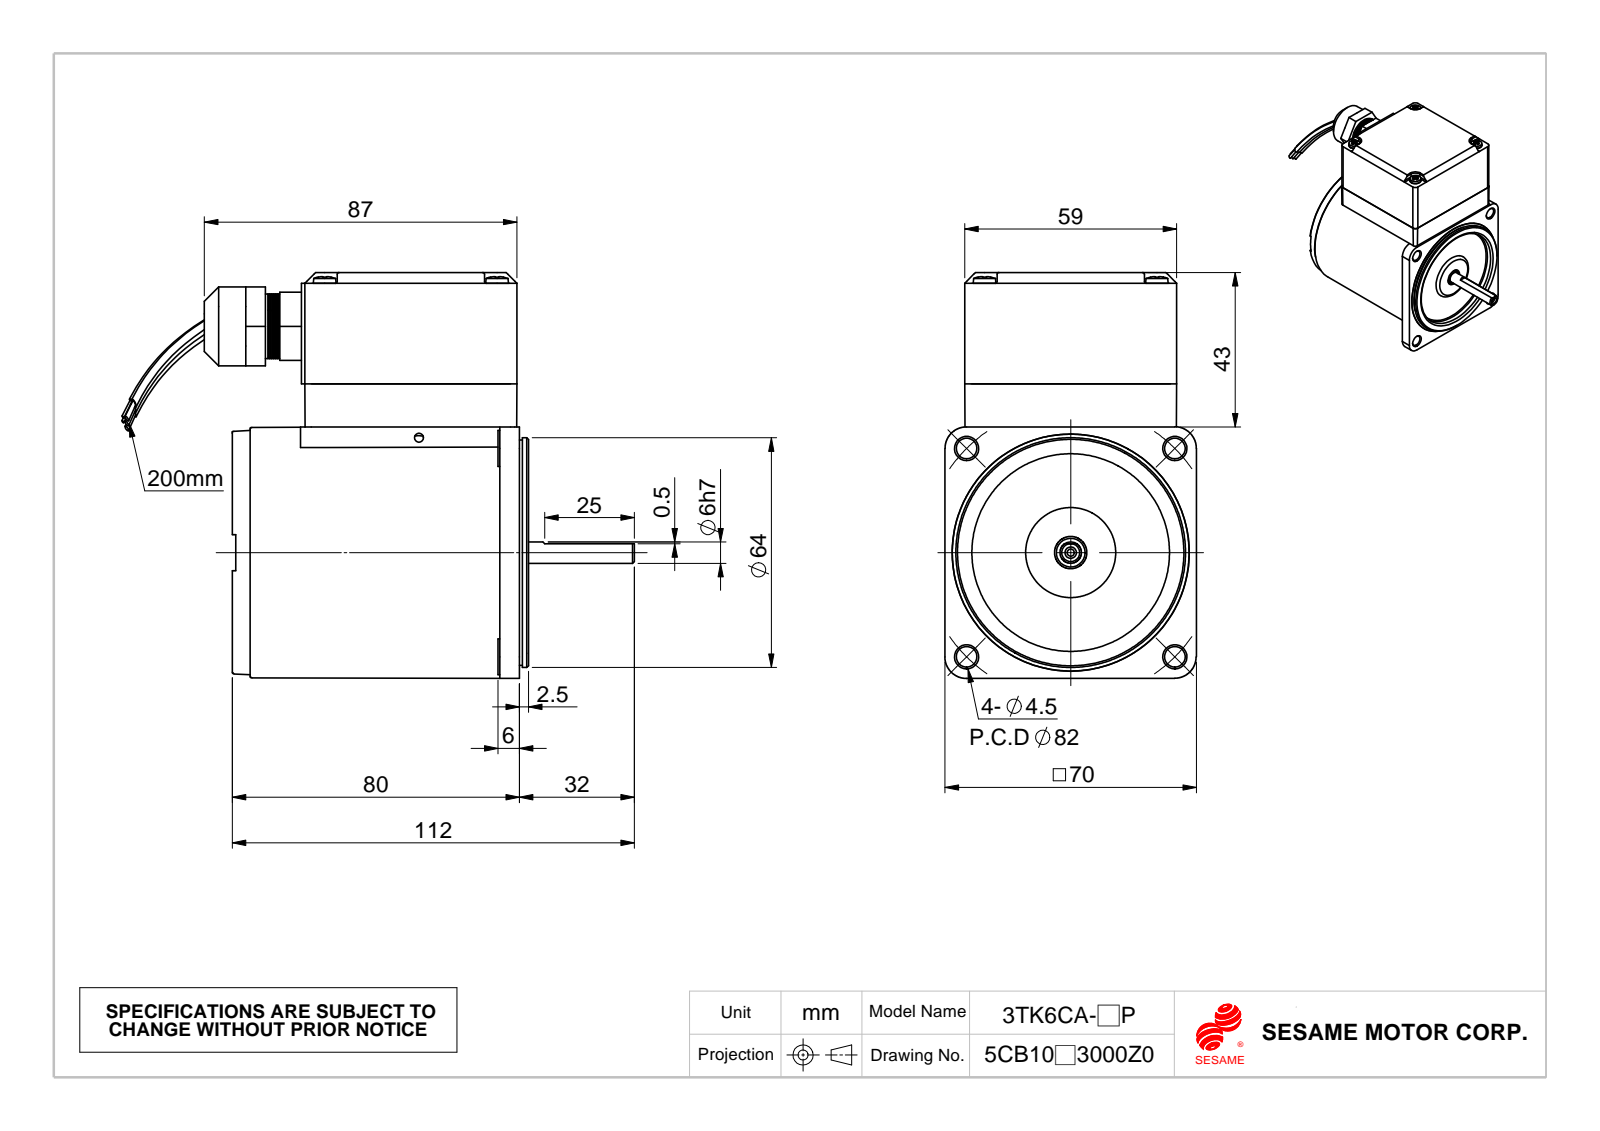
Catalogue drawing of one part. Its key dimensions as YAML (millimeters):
part_name: "成品180度; Ts下墊片; M315Ts_2車工; C364_車工(成品) (+1 more)"
step_written_by: "SolidWorks 2010 (CONFIG_CONTROL_DESIGN)"
units: millimeters
bodies: {solids: 14, faces: 2427, planar: 216, cylindrical: 804, other: 1407}
overall_size: [142.72, 113, 70]
volume: 469849
surface_area: 74287
round_holes:
  - {diameter: 3.3, count: 4}
  - {diameter: 3.5, count: 4}
  - {diameter: 3.9, count: 4}
  - {diameter: 4.3, count: 4}
  - {diameter: 5.75, count: 4}
  - {diameter: 2, count: 1}
  - {diameter: 2.5, count: 1}
  - {diameter: 9, count: 1}
  - {diameter: 11, count: 1}
  - {diameter: 12, count: 1}
  - {diameter: 14.5, count: 1}
  - {diameter: 18, count: 1}
round_bosses_or_shafts:
  - {diameter: 10, count: 5}
  - {diameter: 6.3, count: 4}
  - {diameter: 3, count: 4}
  - {diameter: 63.93, count: 1}
  - {diameter: 62.73, count: 1}
  - {diameter: 57.42, count: 1}
  - {diameter: 57.2, count: 1}
  - {diameter: 22, count: 1}
partial_cylinders:
  - {radius: 2, count: 12}
  - {radius: 0.5, count: 8}
  - {radius: 4, count: 6}
  - {radius: 1.5, count: 4}
  - {radius: 3, count: 4}
  - {radius: 3.5, count: 4}
  - {radius: 6, count: 4}
  - {radius: 34.25, count: 1}
face_to_face_distances: [12, 0.75, 77.4, 31, 1.5, 77.5, 43, 59, 75.89, 1.51]
hole_center_spacings: [41.01, 48, 58, 11.67, 12.35, 12.7, 24.93, 25]
